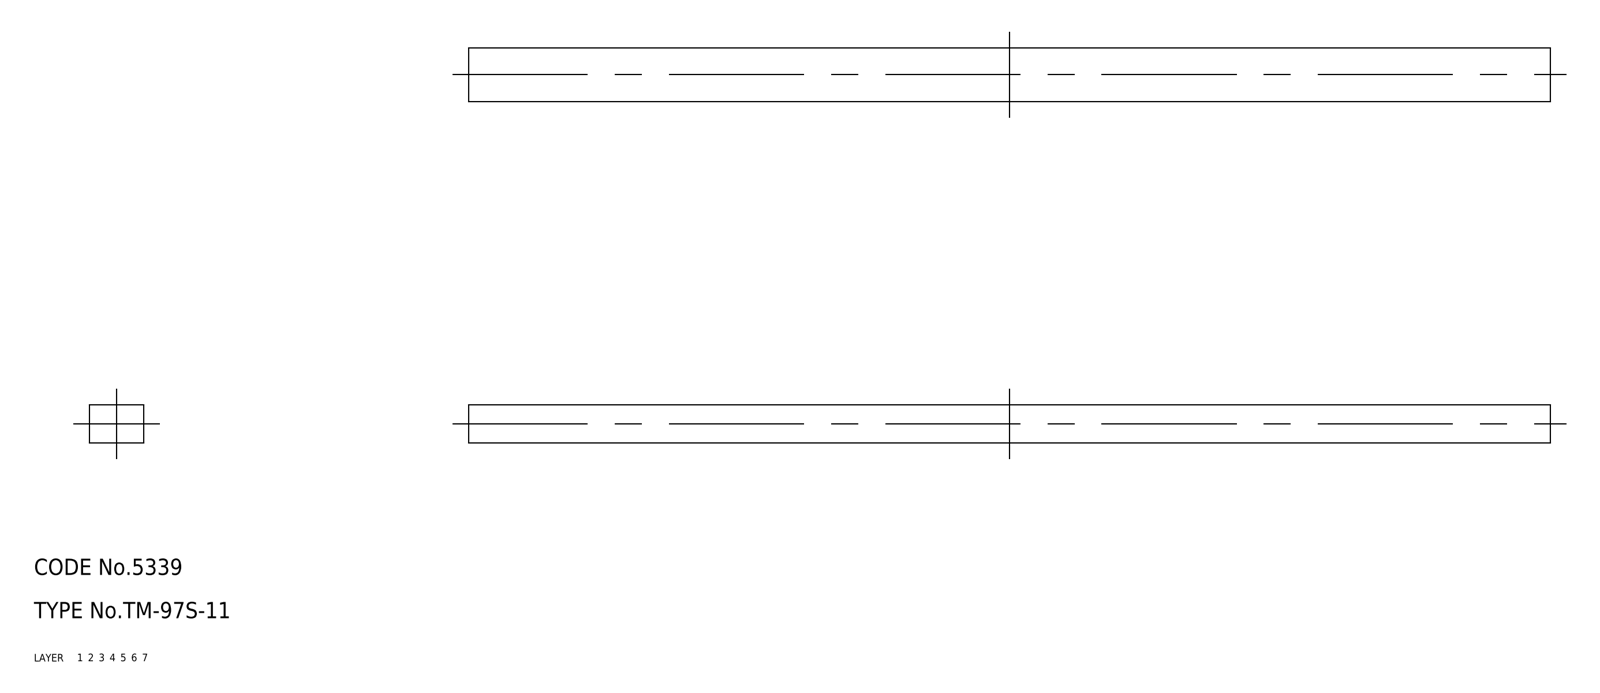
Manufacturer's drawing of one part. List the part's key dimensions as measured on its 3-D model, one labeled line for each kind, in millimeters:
Part name (STEP PRODUCT): rubber foam
STEP written by: CADfix (AUTOMOTIVE_DESIGN)
Units: millimetres
Bodies: 1 solid, 6 faces (0 planar, 0 cylindrical, 6 other)
Overall size (bounding box): 200 × 10 × 7
Volume: 14 000 mm³ · Surface area: 6 940 mm²
